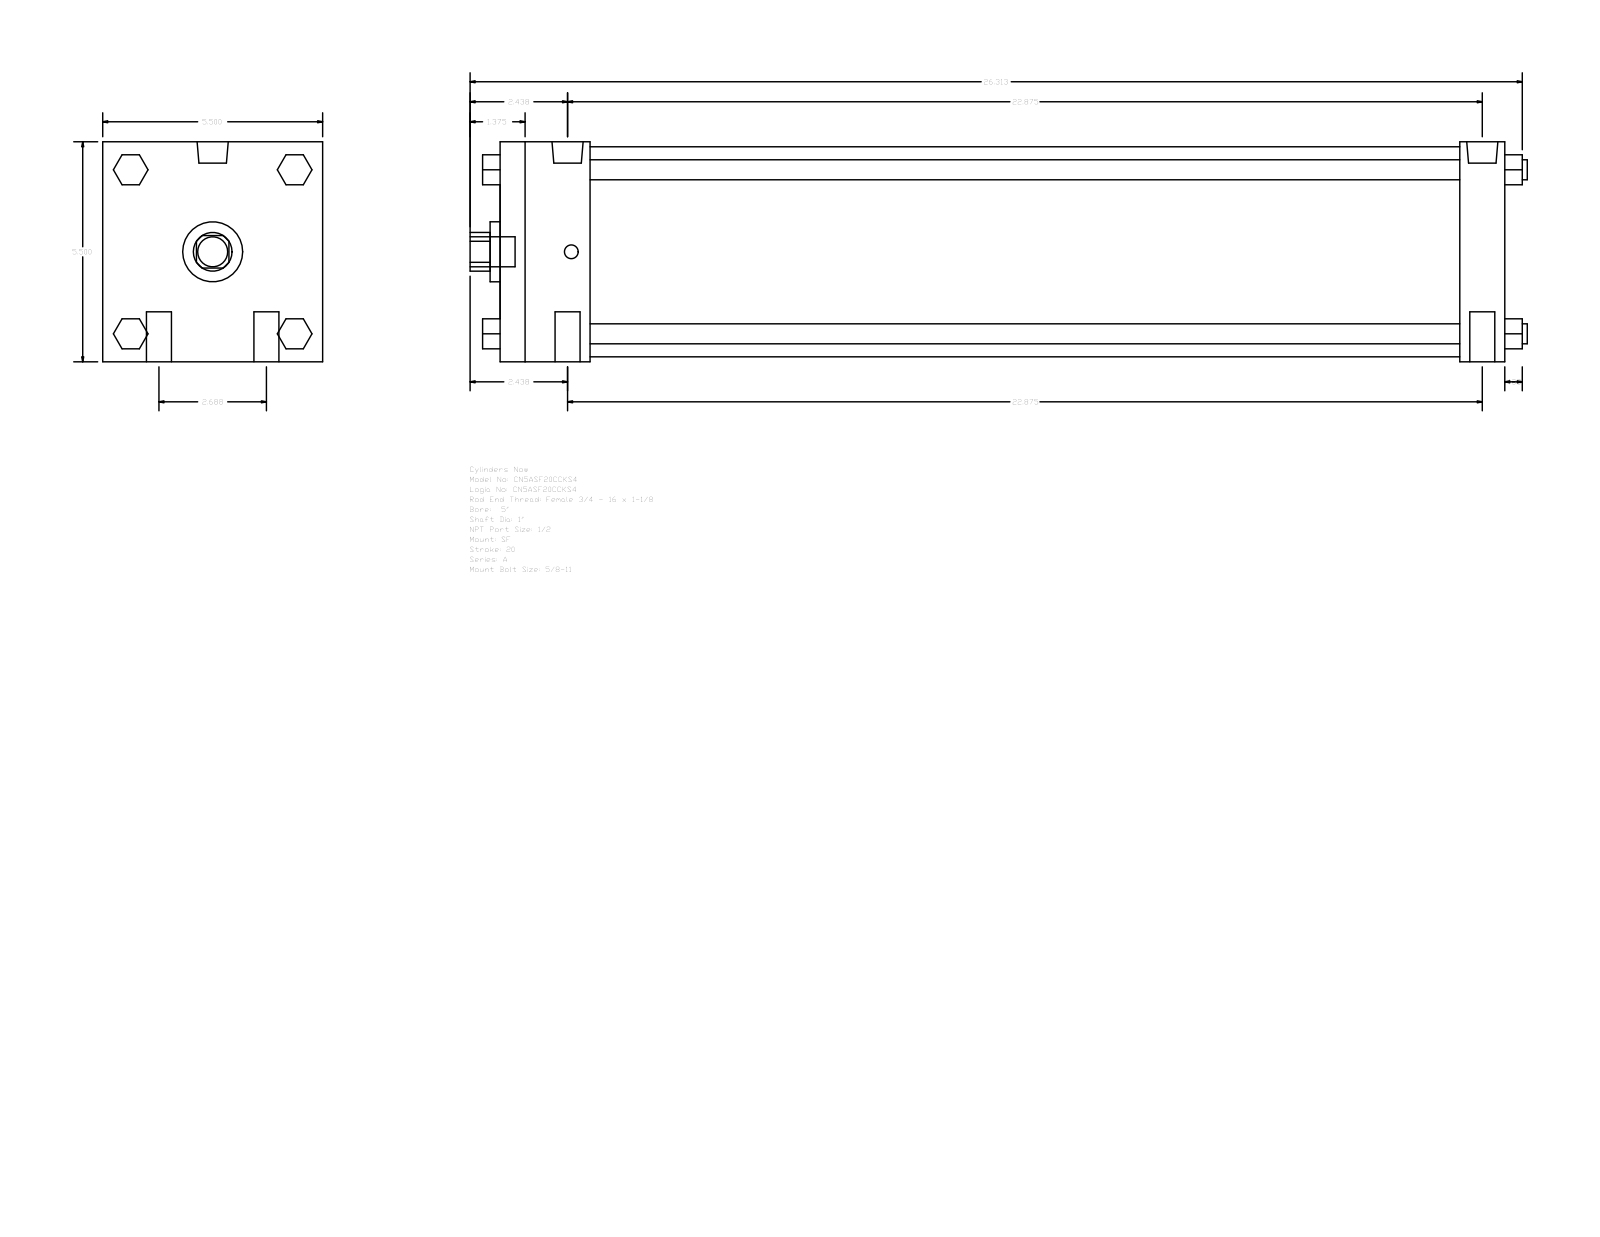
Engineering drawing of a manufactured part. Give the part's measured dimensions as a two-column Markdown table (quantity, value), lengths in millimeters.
| quantity | value |
| --- | --- |
| part name | A_SF__0500_1 |
| STEP written by | GSSL Pune (CONFIG_CONTROL_DESIGN) |
| units | millimeters |
| bodies | 0 solids, 124 faces (94 planar, 30 cylindrical, 0 other) |
| overall size | 671.51 × 139.7 × 139.7 |
| round holes (diameter × count) | 25.4 × 1, 38.1 × 1, 133.35 × 1 |
| round bosses / shafts (diameter × count) | 15.88 × 4, 12.7 × 4, 19.77 × 2, 8.73 × 2, 19.05 × 1 |
| partial cylindrical surfaces (radius × count) | 12.29 × 1 |
| main face-to-face distances | 139.7, 638.18, 57.15, 609.6, 552.45, 581.03, 28.58, 19.05, 52.07, 90.18 |
